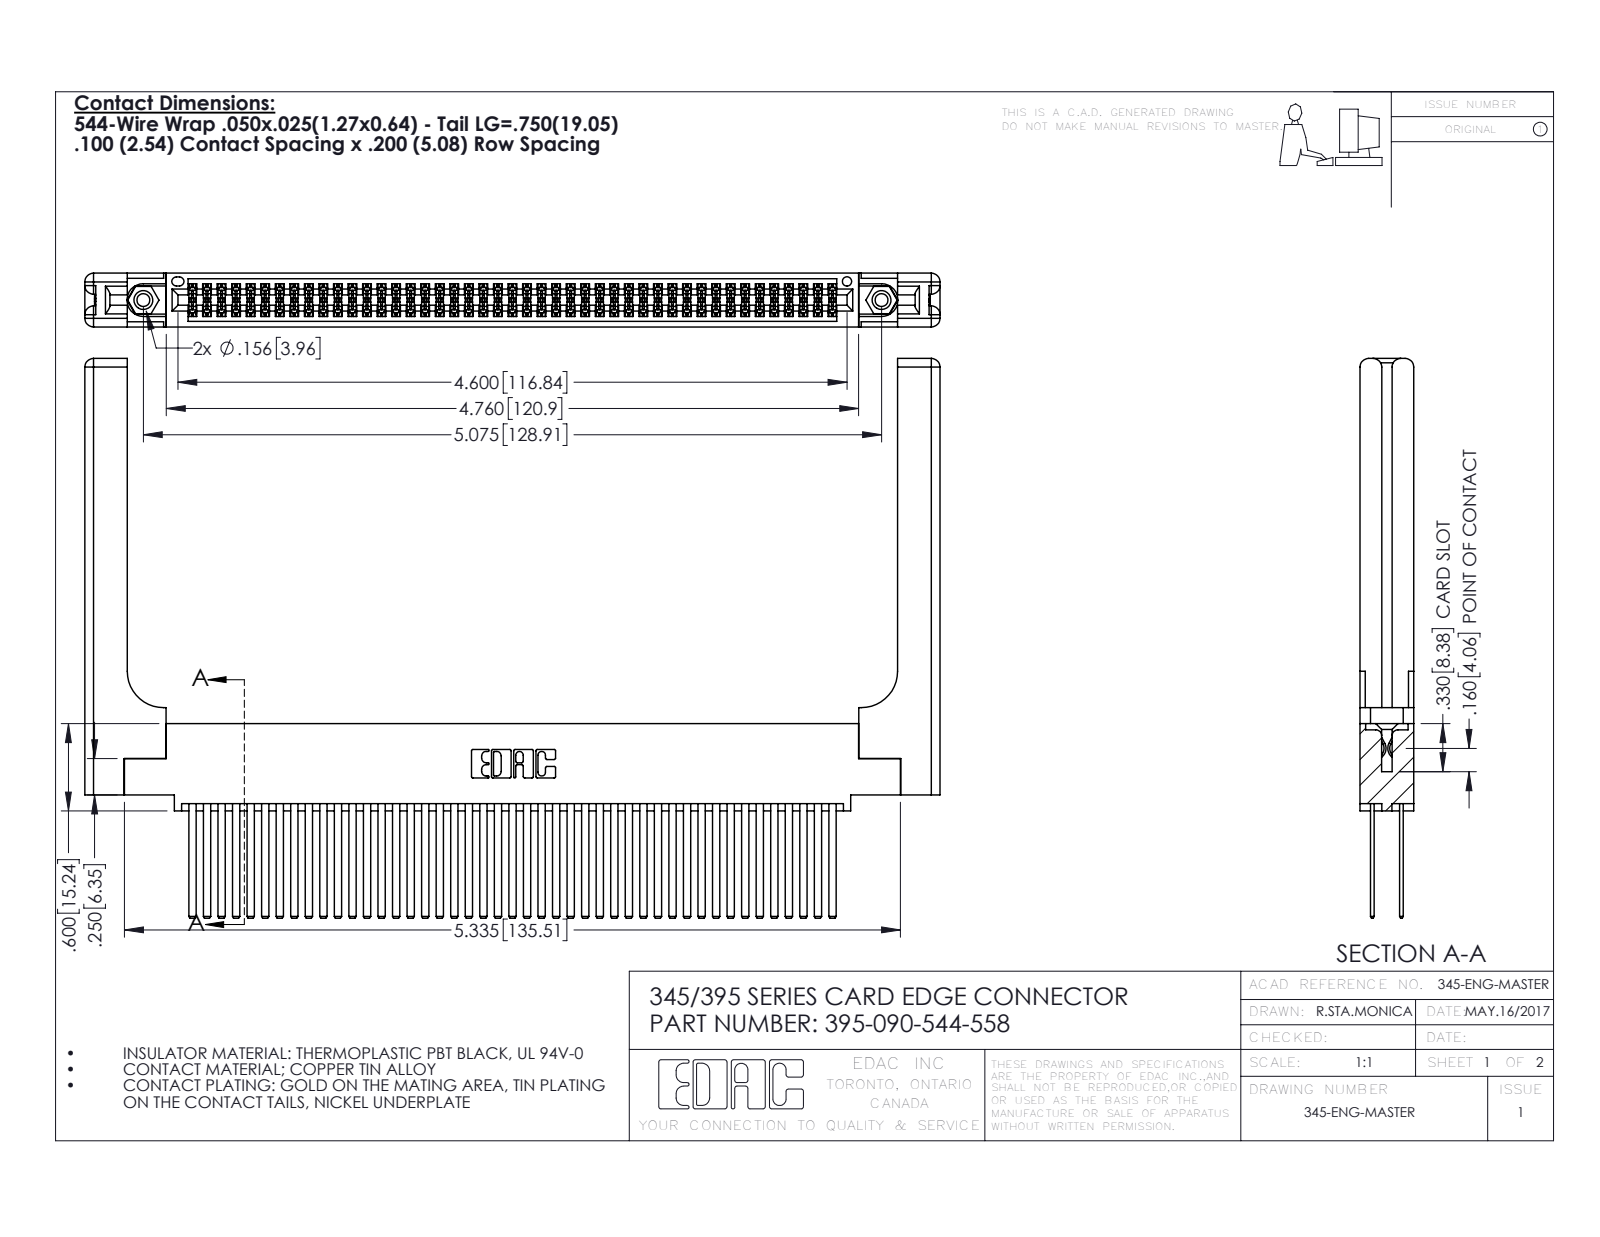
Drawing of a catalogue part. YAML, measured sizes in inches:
part_name: "345 Part_0.110 Offset - 0.156 Dia-TH; 345-250-001_345-250-001-102; 395-090-544-558; 345-220-058_345-220-058 (+1 more)"
step_written_by: "SolidWorks 2016 (CONFIG_CONTROL_DESIGN)"
units: inches
bodies: {solids: 95, faces: 4346, planar: 2842, cylindrical: 1444, other: 60}
overall_size: [5.879, 3.847, 0.37]
volume: 1.477
surface_area: 49.83
round_holes:
  - {diameter: 0.089, count: 2}
  - {diameter: 0.125, count: 2}
  - {diameter: 0.156, count: 2}
  - {diameter: 0.064, count: 1}
round_bosses_or_shafts:
  - {diameter: 0.155, count: 2}
partial_cylinders:
  - {radius: 0.006, count: 135}
  - {radius: 0.01, count: 22}
  - {radius: 0.06, count: 16}
  - {radius: 0.007, count: 6}
  - {radius: 0.031, count: 6}
  - {radius: 0.026, count: 3}
  - {radius: 0.014, count: 2}
  - {radius: 0.019, count: 2}
face_to_face_distances: [0.072, 0.298, 0.098, 0.272, 0.025, 0.2, 0.37, 0.225, 0.175, 0.148]
hole_center_spacings: [0.27, 4.839, 5.075]
